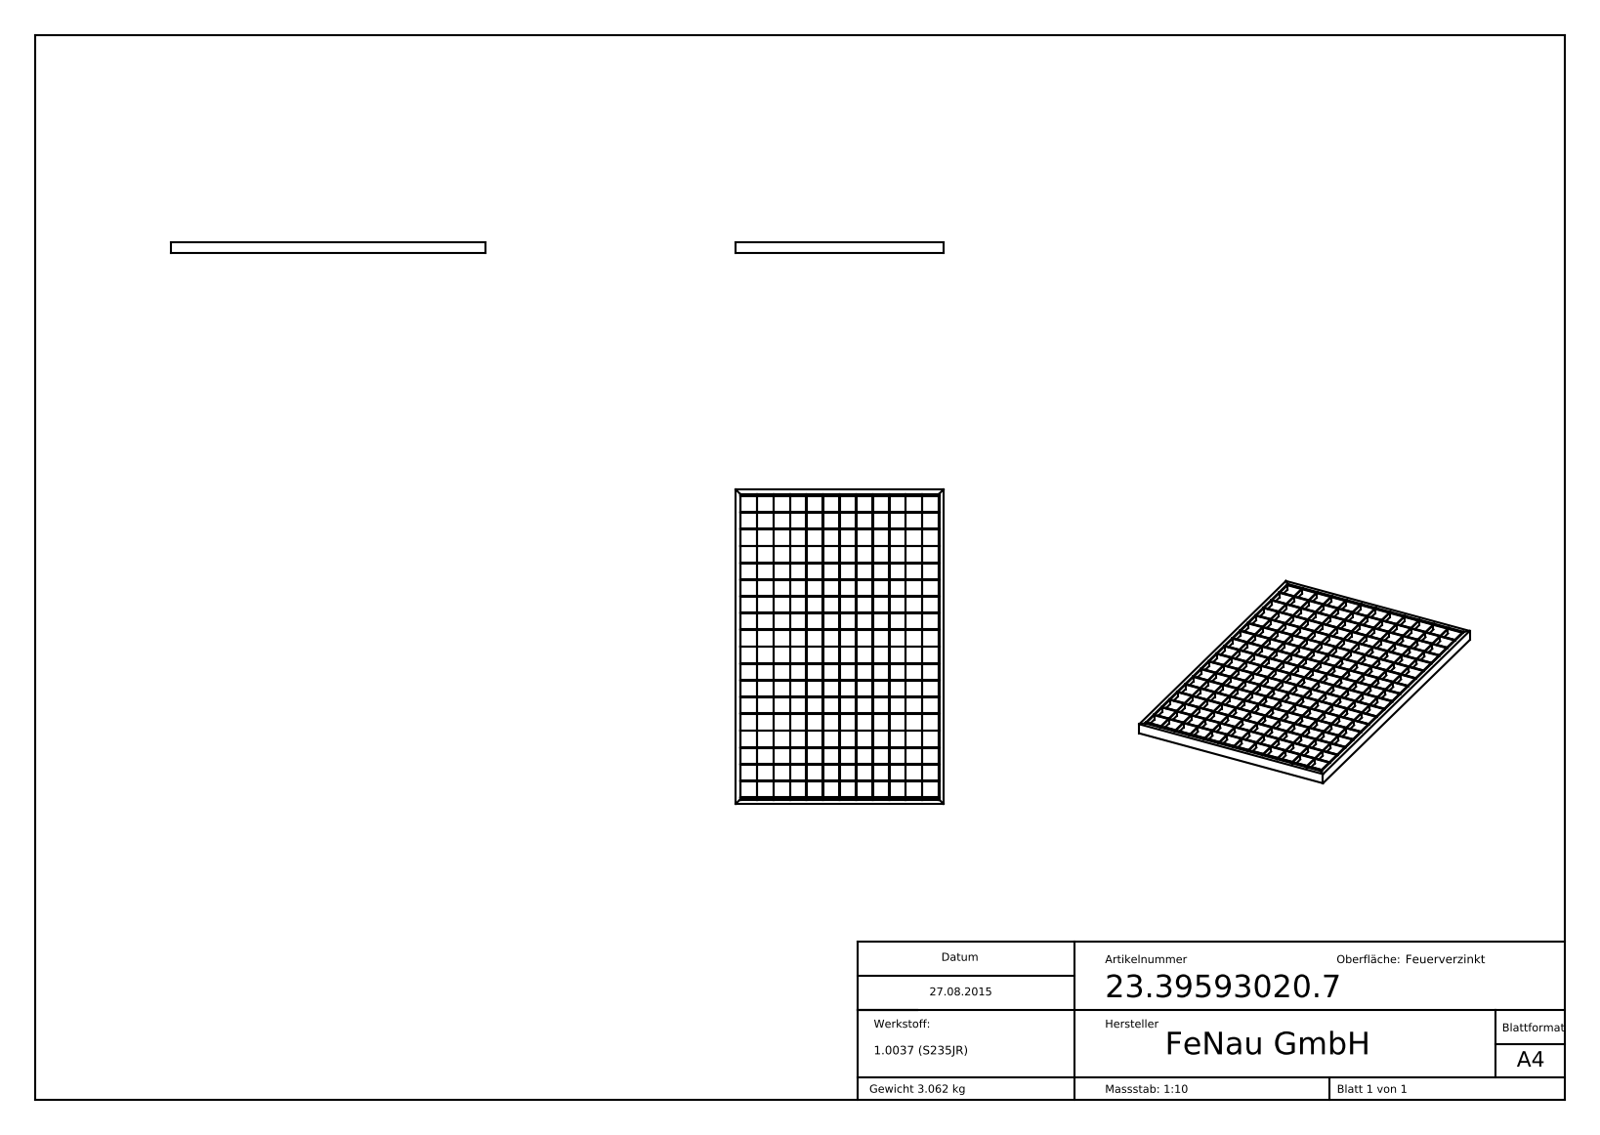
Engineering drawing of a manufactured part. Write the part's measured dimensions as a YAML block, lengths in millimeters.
part_name: "23-39593020-7"
step_written_by: "SolidWorks 2015 (CONFIG_CONTROL_DESIGN)"
units: millimeters
bodies: {solids: 1, faces: 1004, planar: 1004, cylindrical: 0, other: 0}
overall_size: [590, 390, 20]
volume: 392619
surface_area: 574767
face_to_face_distances: [63, 31.5, 94.5, 126, 157.5, 189, 220.5, 252, 31, 283.5]
